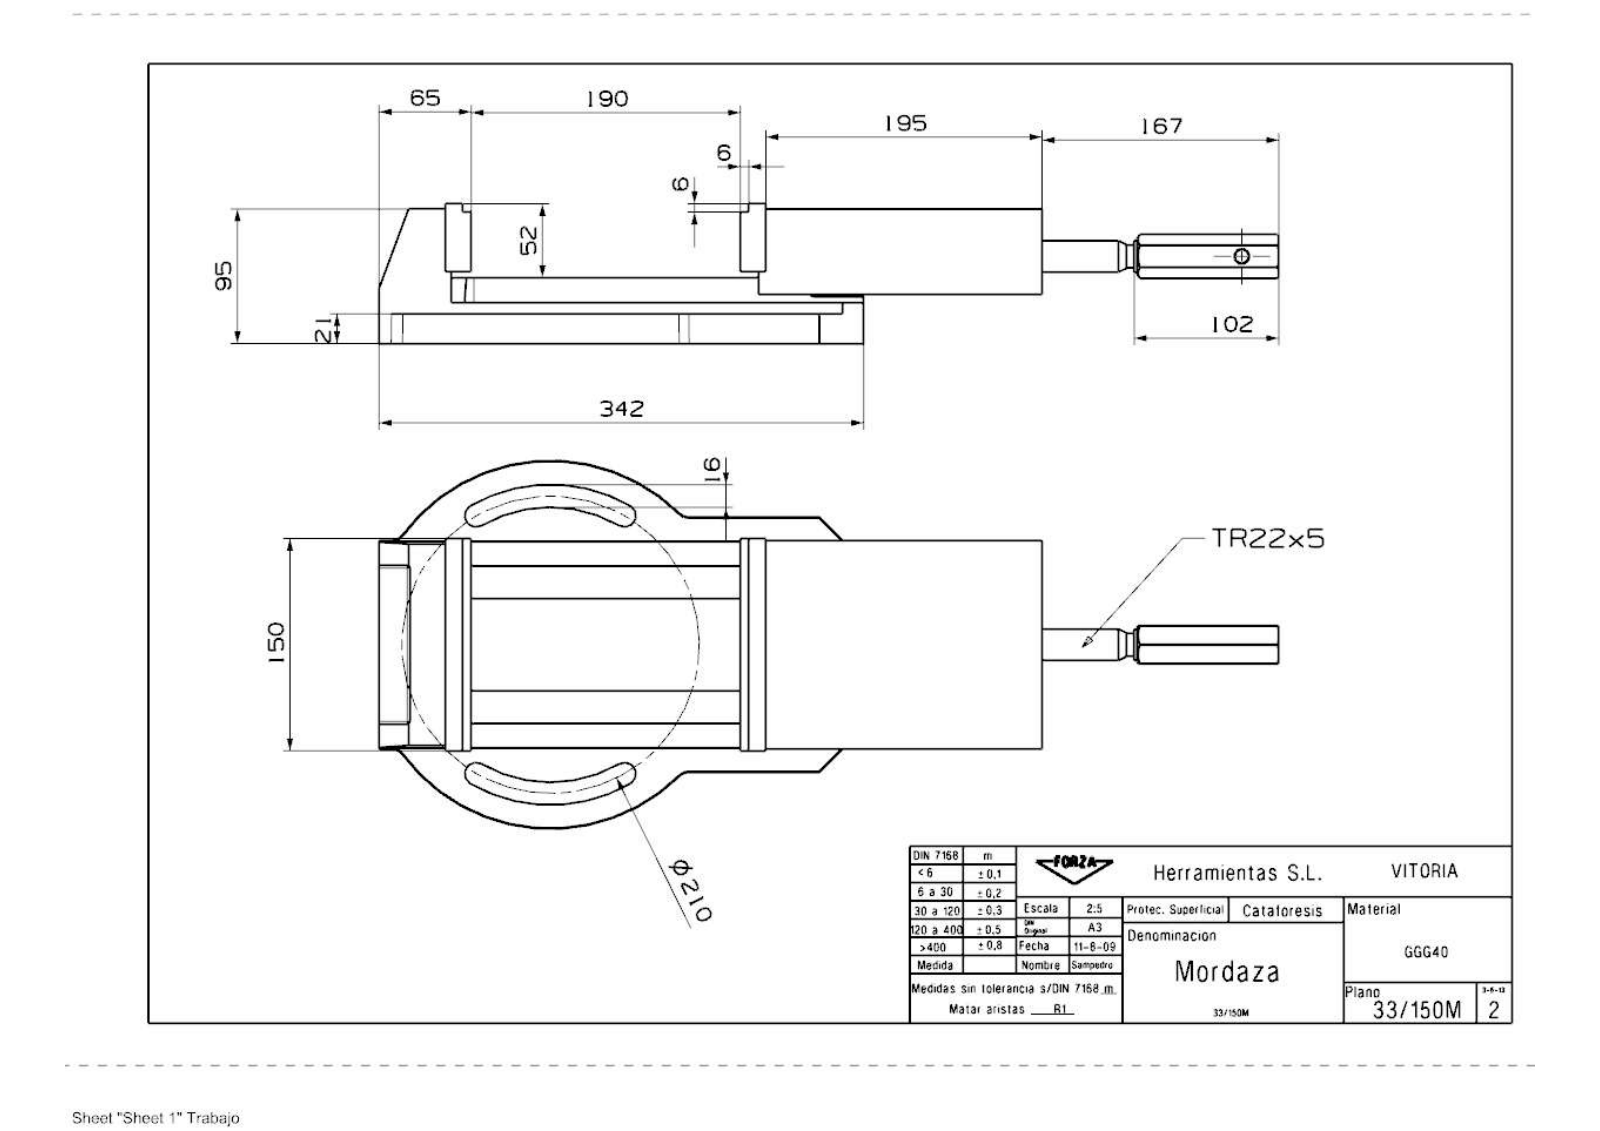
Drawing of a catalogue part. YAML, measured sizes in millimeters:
part_name: "33_150M_Mordaza"
step_written_by: "SIEMENS PLM Software NX 9.0 (CONFIG_CONTROL_DESIGN)"
units: millimeters
bodies: {solids: 6, faces: 222, planar: 116, cylindrical: 72, other: 34}
overall_size: [635, 259.89, 98.75]
volume: 2855000
surface_area: 414063
round_holes:
  - {diameter: 6.99, count: 3}
  - {diameter: 10, count: 3}
  - {diameter: 8.5, count: 2}
  - {diameter: 8.78, count: 2}
  - {diameter: 10.5, count: 2}
  - {diameter: 17, count: 2}
  - {diameter: 8, count: 1}
  - {diameter: 18, count: 1}
  - {diameter: 19.25, count: 1}
round_bosses_or_shafts:
  - {diameter: 22, count: 1}
  - {diameter: 17, count: 1}
  - {diameter: 16, count: 1}
  - {diameter: 12, count: 1}
partial_cylinders:
  - {radius: 2, count: 13}
  - {radius: 10, count: 8}
  - {radius: 3, count: 4}
  - {radius: 8, count: 4}
  - {radius: 17, count: 2}
  - {radius: 15.5, count: 1}
  - {radius: 75, count: 1}
  - {radius: 97, count: 1}
face_to_face_distances: [94.8, 10, 15, 17.5, 80, 18, 41, 84.8, 73.8, 63.8]
hole_center_spacings: [19.24, 39.77, 39.84, 35, 75]
